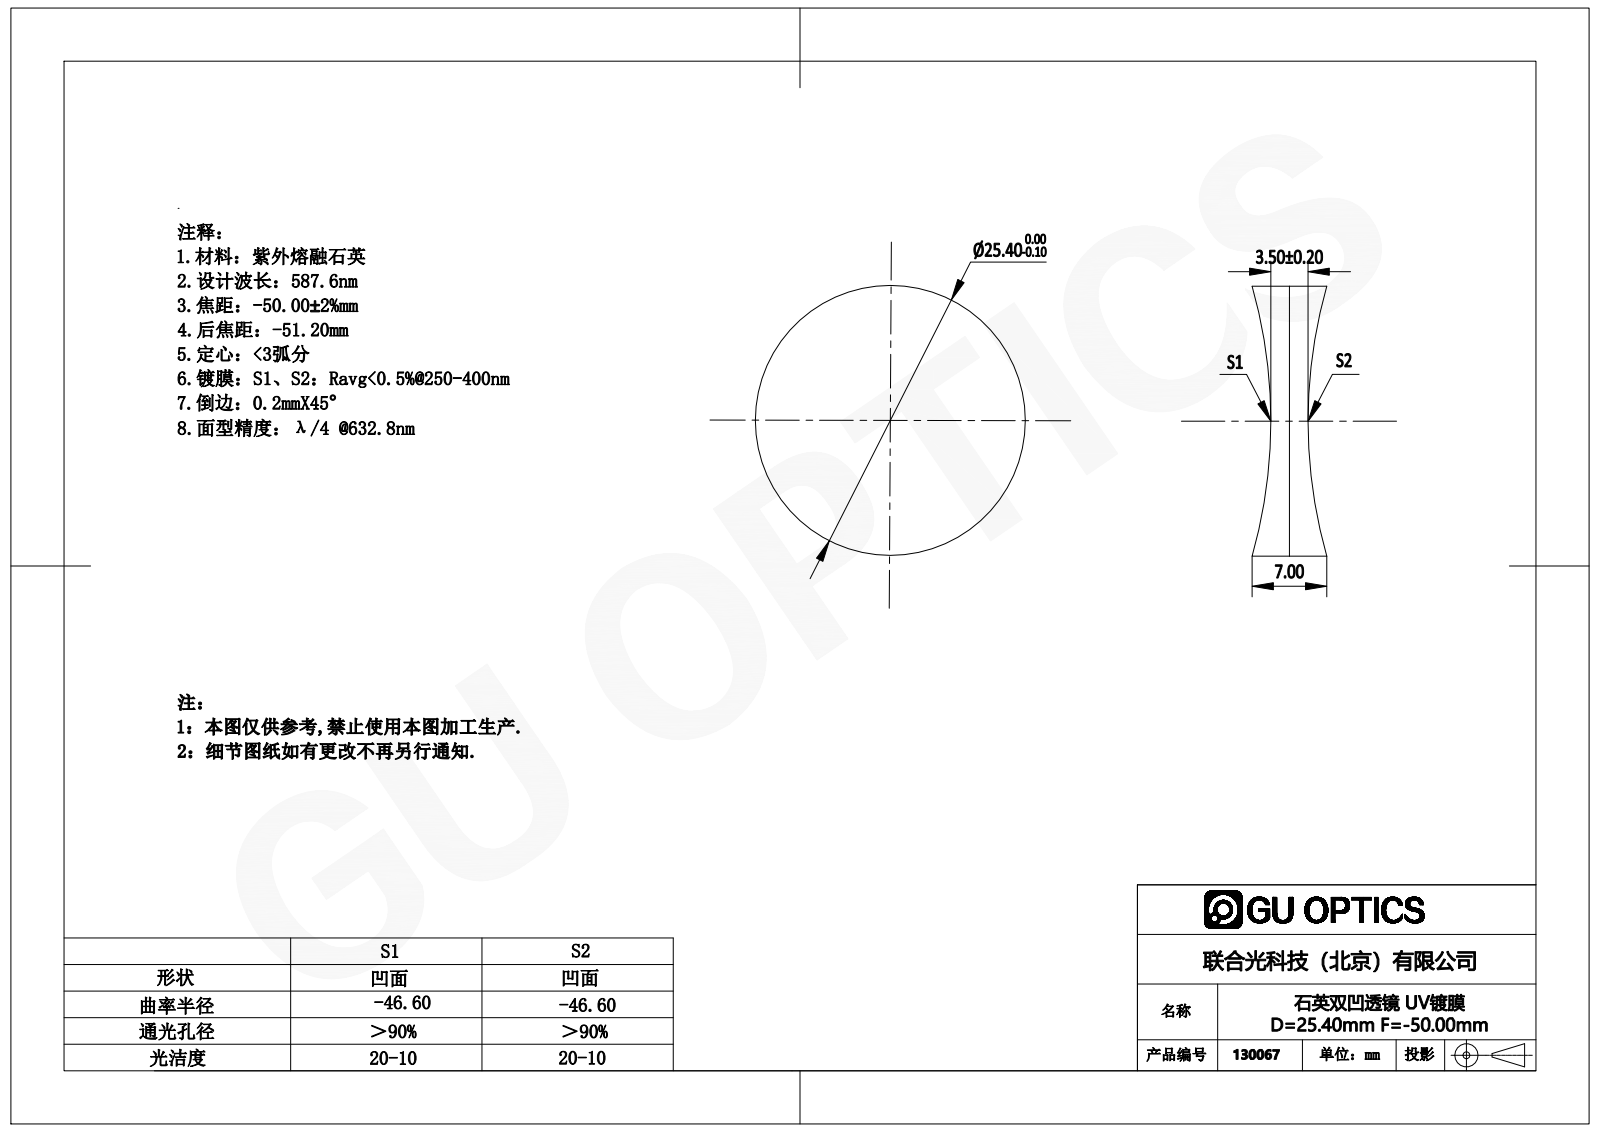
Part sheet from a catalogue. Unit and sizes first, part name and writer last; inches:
Units: inches
Overall size (bounding box): 1 × 1 × 0.277
Round bosses / shafts (diameter × count): ⌀1 ×1
Volume: 0.162 in³ · Surface area: 2.471 in²
Bodies: 1 solid, 6 faces (0 planar, 2 cylindrical, 4 other)
Part name (STEP PRODUCT): 130058
STEP written by: SolidWorks 2016 (AUTOMOTIVE_DESIGN)
